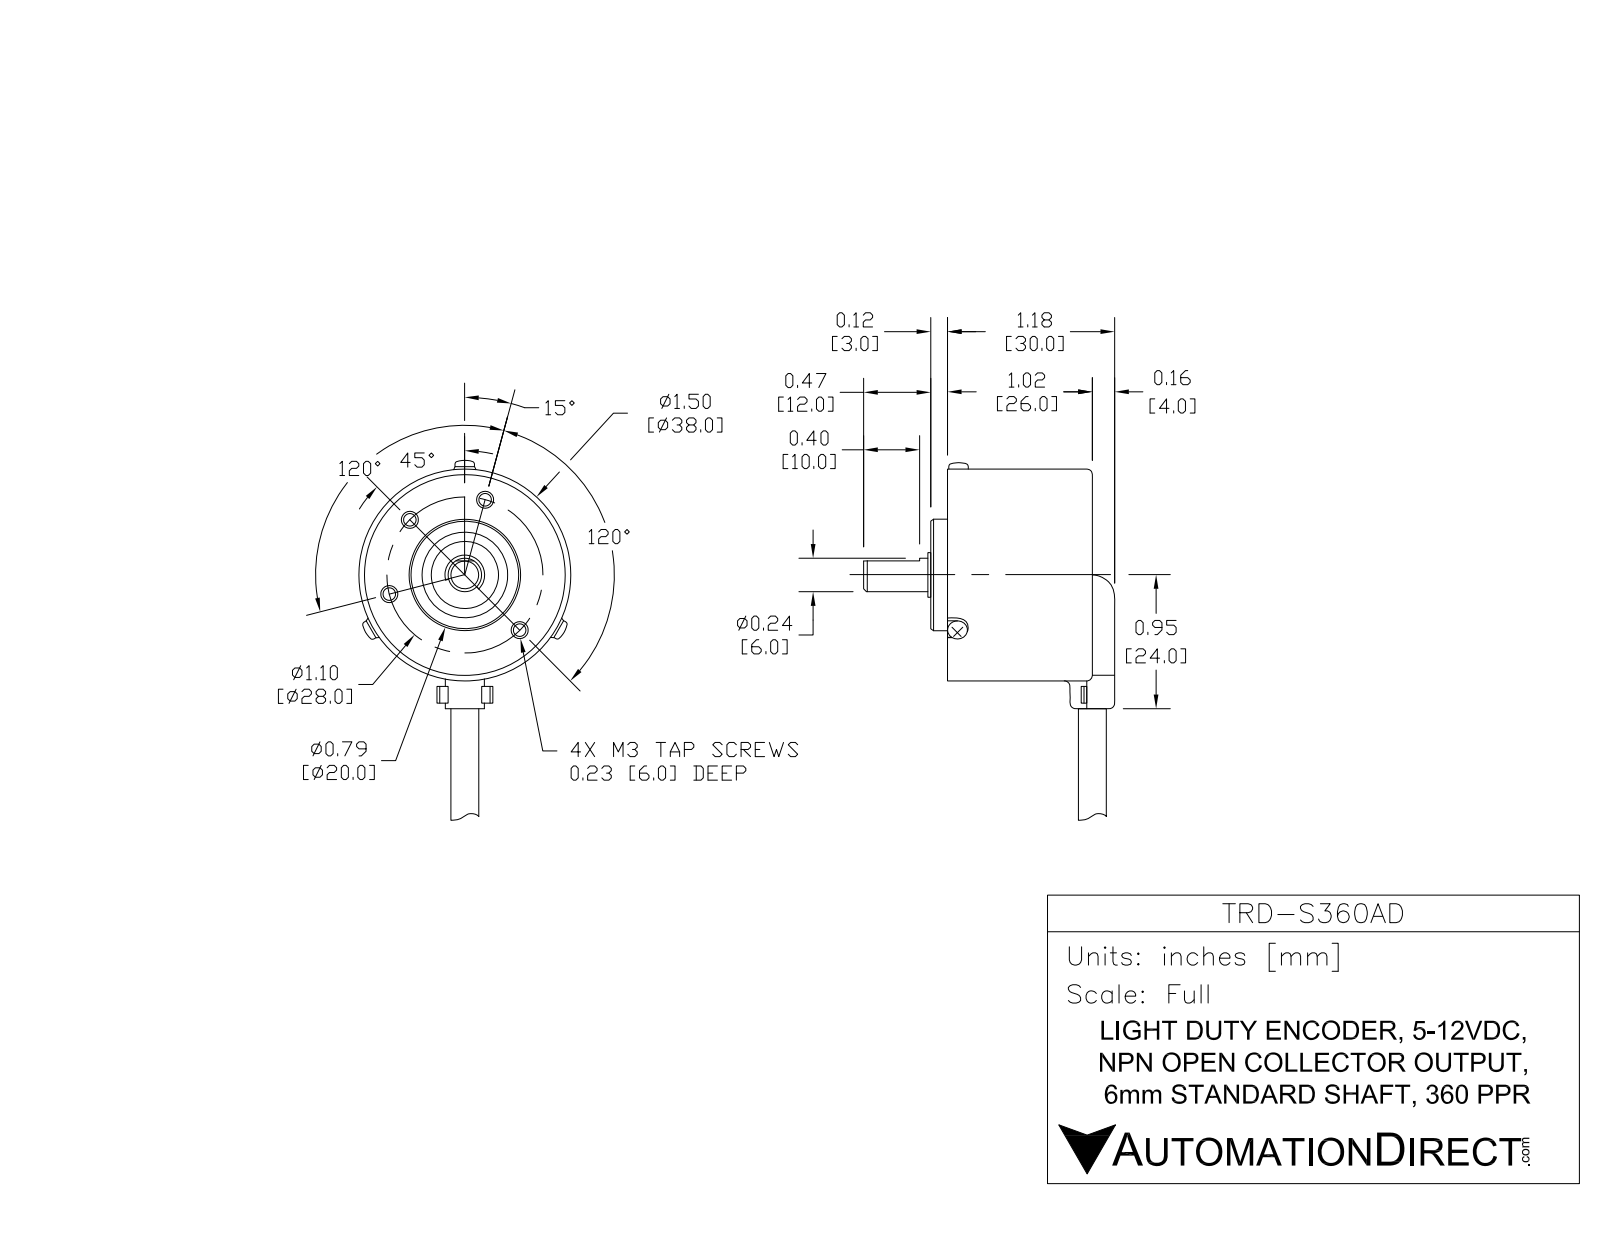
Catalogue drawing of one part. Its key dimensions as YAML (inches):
part_name: "TRD-S360AD"
step_written_by: "SolidWorks 2016 (AUTOMOTIVE_DESIGN)"
units: inches
bodies: {solids: 3, faces: 257, planar: 98, cylindrical: 100, other: 59}
overall_size: [7.189, 1.768, 1.496]
volume: 2.068
surface_area: 13.85
round_holes:
  - {diameter: 0.118, count: 4}
  - {diameter: 0.205, count: 1}
  - {diameter: 0.256, count: 1}
  - {diameter: 1.409, count: 1}
round_bosses_or_shafts:
  - {diameter: 1.496, count: 1}
  - {diameter: 0.787, count: 1}
  - {diameter: 0.591, count: 1}
  - {diameter: 0.315, count: 1}
  - {diameter: 0.236, count: 1}
  - {diameter: 0.197, count: 1}
  - {diameter: 0.193, count: 1}
partial_cylinders:
  - {radius: 0.016, count: 11}
  - {radius: 0.004, count: 4}
  - {radius: 0.13, count: 3}
  - {radius: 0.748, count: 3}
  - {radius: 0.008, count: 2}
  - {radius: 0.02, count: 2}
  - {radius: 0.146, count: 2}
  - {radius: 0.11, count: 1}
face_to_face_distances: [1.024, 0.118, 1.142, 0.02, 0.138, 0.803, 1.161, 0.354, 0.335, 0.217]
hole_center_spacings: [0.551, 0.955, 0.954, 1.102]
